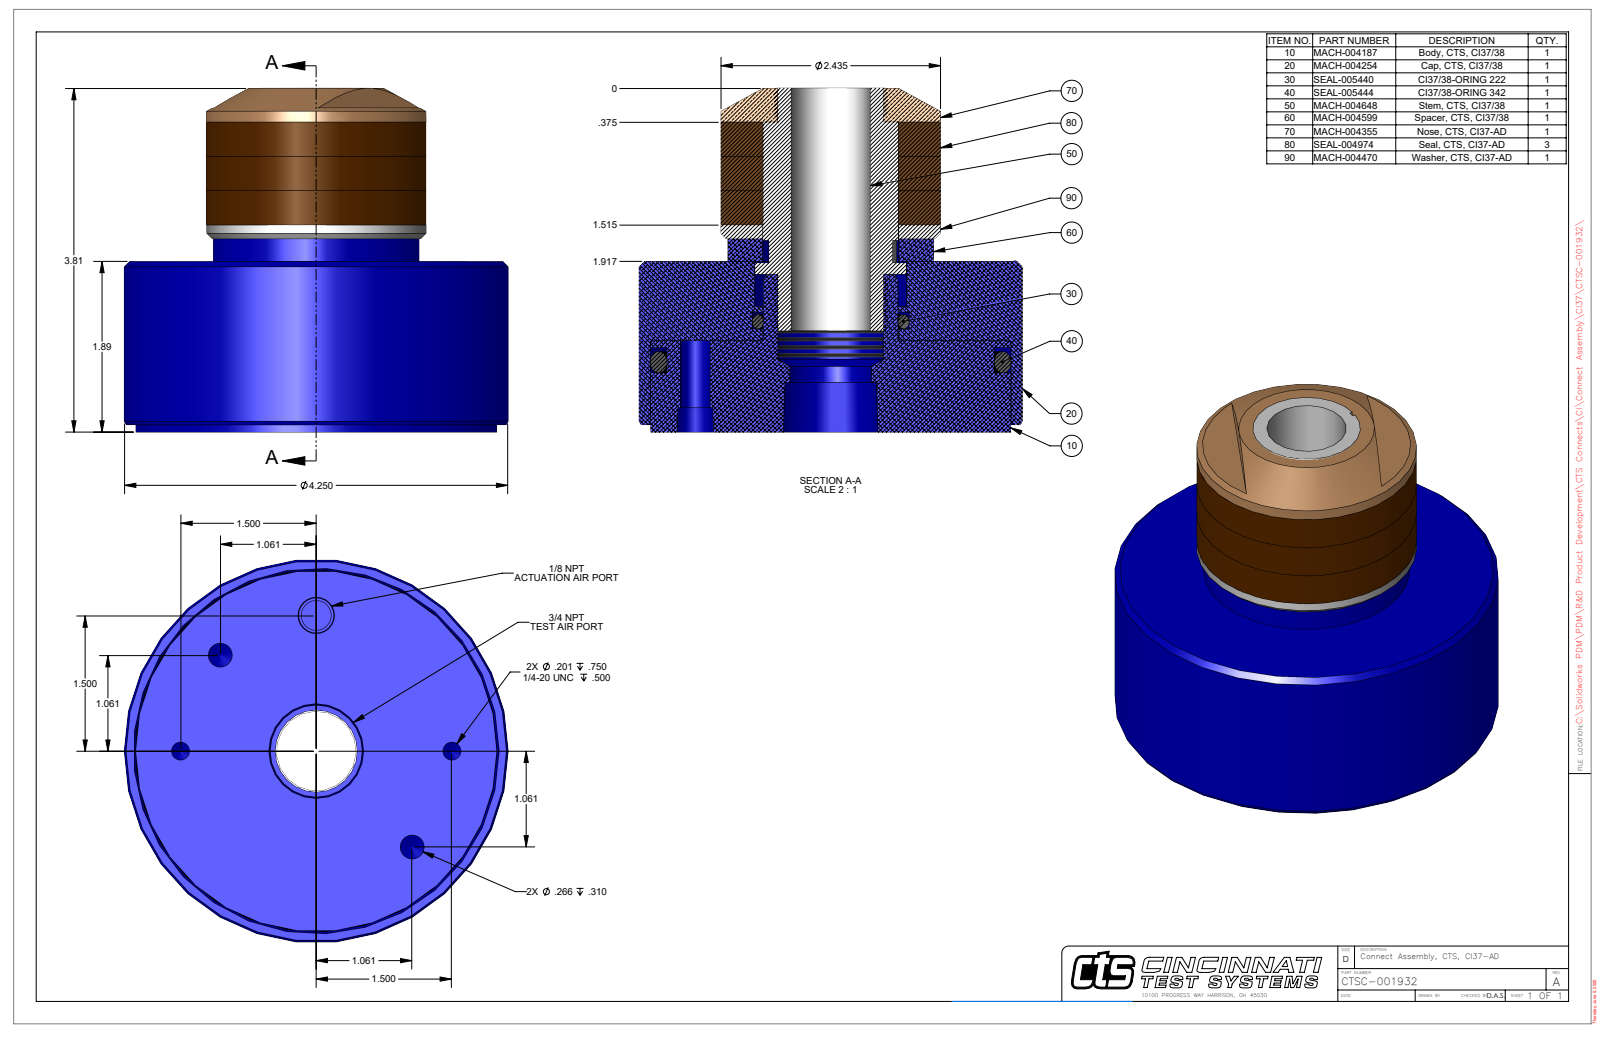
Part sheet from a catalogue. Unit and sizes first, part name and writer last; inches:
Units: inches
Overall size (bounding box): 4.25 × 4.25 × 3.813
Round holes (diameter × count): ⌀0.201 ×2, ⌀0.266 ×2, ⌀0.332 ×1, ⌀0.88 ×1, ⌀1.51 ×1, ⌀1.688 ×1, ⌀4 ×1
Round bosses / shafts (diameter × count): ⌀4.25 ×1, ⌀3.992 ×1, ⌀2.435 ×1, ⌀2.281 ×1, ⌀1.674 ×1, ⌀1.5 ×1
Partial cylindrical surfaces — rounded edges, fillets, slot ends (radius × count): R0.586 ×1
Main face-to-face distances: 1.893, 0.083, 1.81, 3.591, 3.508, 1.698, 3.81, 3.727, 1.917, 0.219
Hole centre spacings: 1.5, 1.148, 2.772, 2.121, 3
Volume: 32.52 in³ · Surface area: 93.01 in²
Bodies: 2 solids, 83 faces (28 planar, 31 cylindrical, 24 other)
Part name (STEP PRODUCT): CTSC-001932
STEP written by: SolidWorks 2023 (AUTOMOTIVE_DESIGN)
